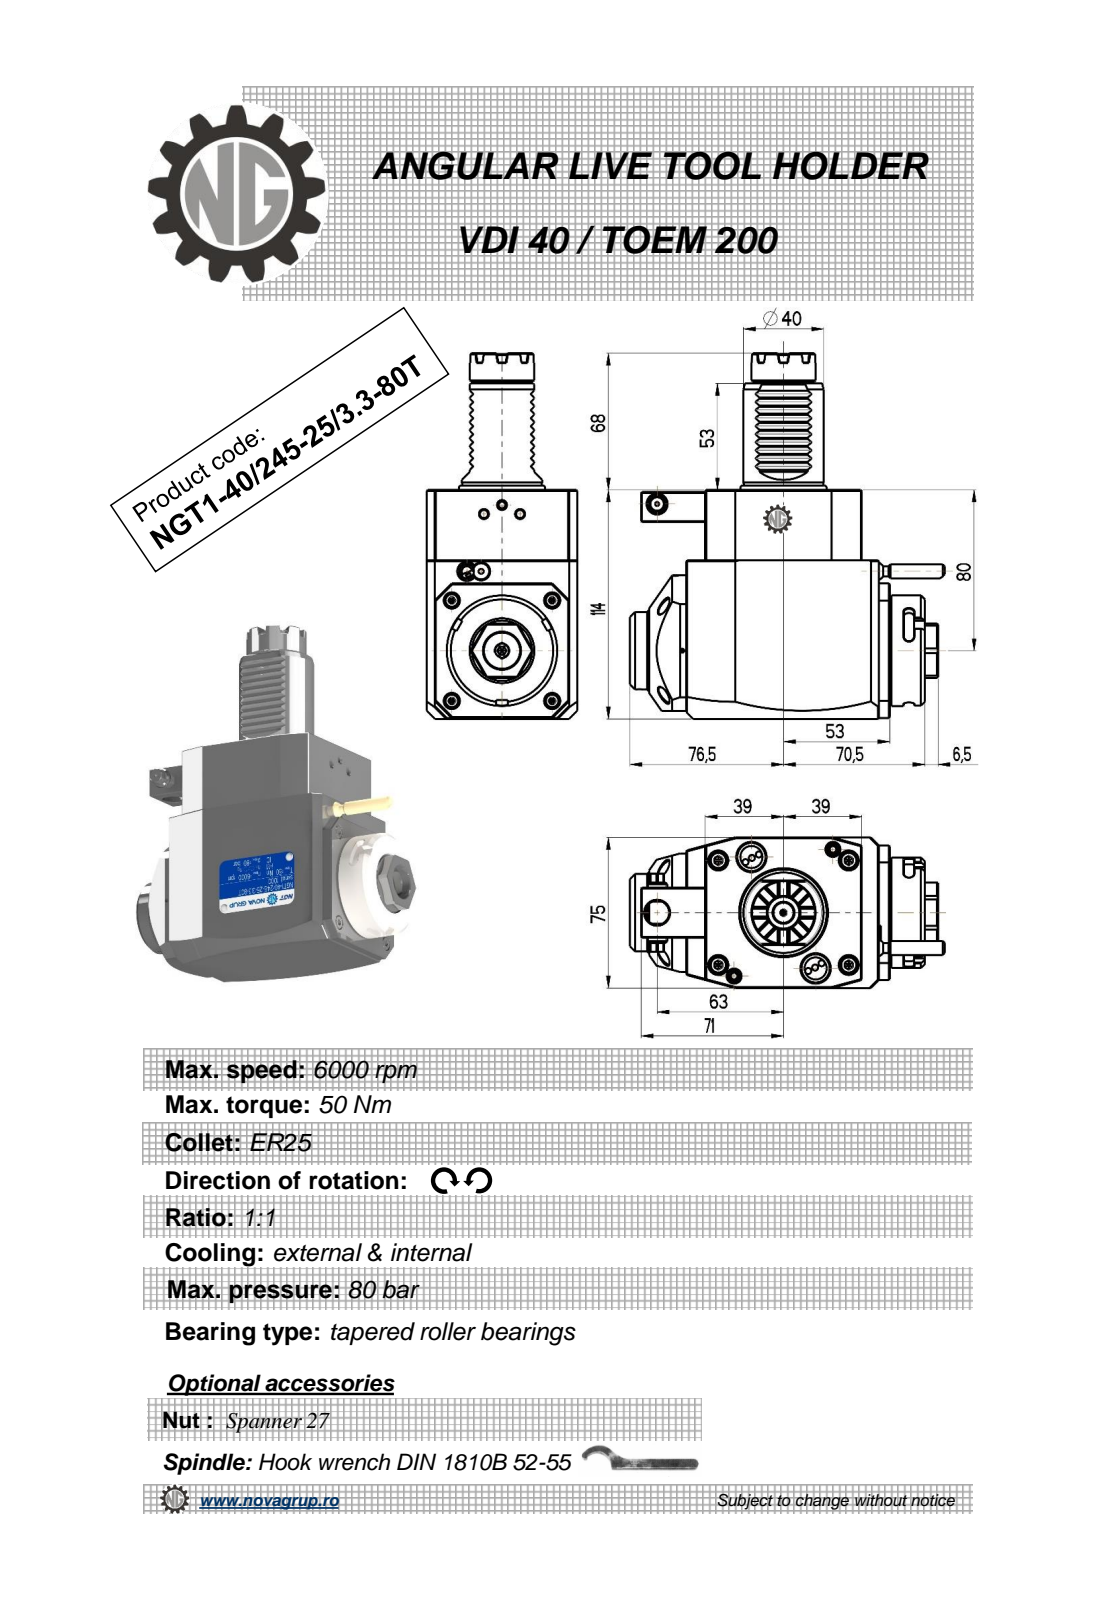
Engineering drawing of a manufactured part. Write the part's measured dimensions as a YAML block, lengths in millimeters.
part_name: "NGT1_40_245_25_3_3_80T"
step_written_by: "PRO/ENGINEER BY PARAMETRIC TECHNOLOGY CORPORATION, 2010280 (CONFIG_CONTROL_DESIGN)"
units: millimeters
bodies: {solids: 1, faces: 478, planar: 257, cylindrical: 101, other: 120}
overall_size: [182, 156.83, 75]
volume: 962759
surface_area: 73160
round_holes:
  - {diameter: 2, count: 1}
  - {diameter: 2.5, count: 1}
  - {diameter: 3, count: 1}
  - {diameter: 4.5, count: 1}
  - {diameter: 9.5, count: 1}
  - {diameter: 12, count: 1}
  - {diameter: 18, count: 1}
round_bosses_or_shafts:
  - {diameter: 8, count: 2}
  - {diameter: 55, count: 1}
  - {diameter: 48, count: 1}
  - {diameter: 40, count: 1}
  - {diameter: 38.5, count: 1}
  - {diameter: 32, count: 1}
  - {diameter: 17.2, count: 1}
  - {diameter: 10, count: 1}
partial_cylinders:
  - {radius: 0.3, count: 20}
  - {radius: 2.5, count: 6}
  - {radius: 180, count: 2}
  - {radius: 3.85, count: 1}
  - {radius: 4.25, count: 1}
  - {radius: 15, count: 1}
  - {radius: 24.5, count: 1}
  - {radius: 37.5, count: 1}
face_to_face_distances: [75, 114, 14, 17.5, 78, 92, 31.5, 109.5, 35, 4]
hole_center_spacings: [37.35, 43.2, 72.5]
